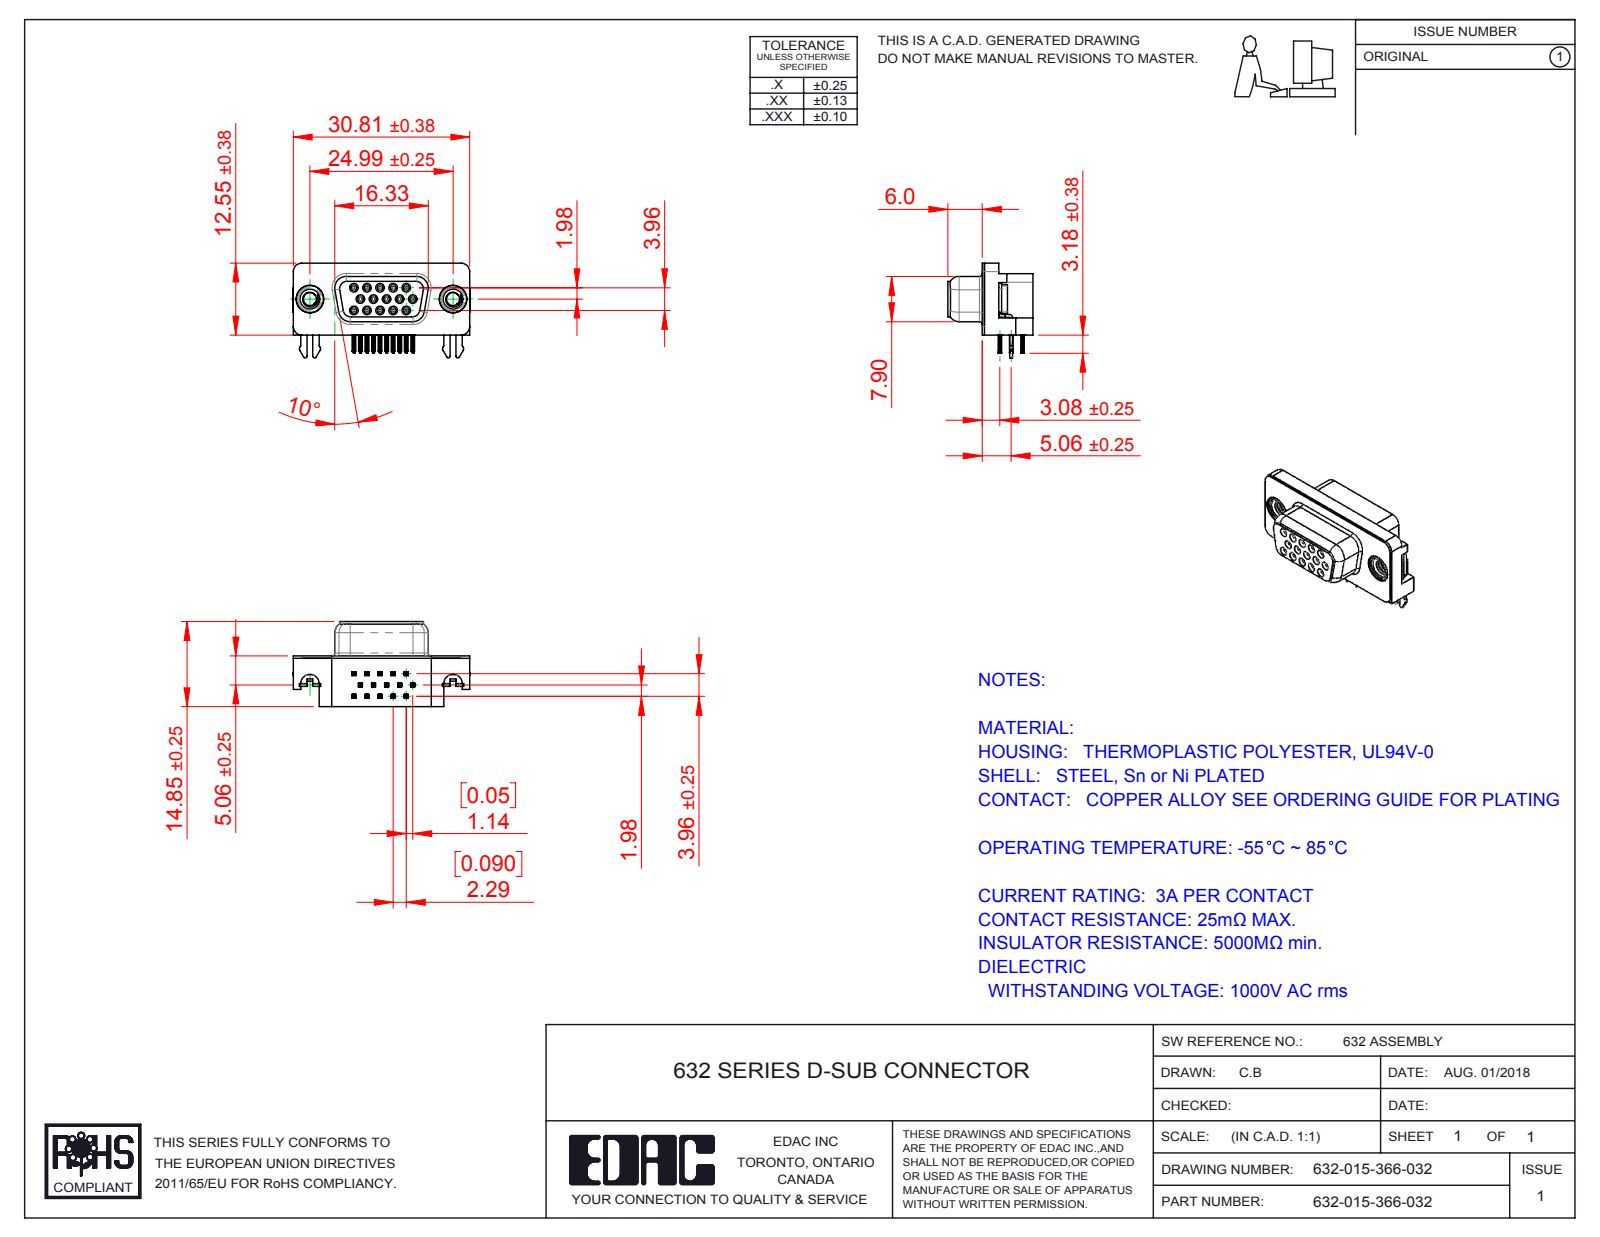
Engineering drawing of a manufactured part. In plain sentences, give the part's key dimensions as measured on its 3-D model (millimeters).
The part is named "632 Shell_9 Socket; 632 2 Prong Board Lock; 632 4-40 Threaded Rivet; 632 Contact Middle (+4 more)". Its 3-D file was written by "SolidWorks 2016 (CONFIG_CONTROL_DESIGN)". It is 21 solids with 2338 faces: 990 planar, 612 cylindrical and 736 other. Overall it measures 30.89 by 16.55 by 14.85 millimeters. Its volume is 2 921 cubic millimeters and its surface area 5 018 square millimeters. Round holes: 15 of diameter 0.8, 15 of diameter 0.9, 2 of diameter 2.26, 2 of diameter 4, 2 of diameter 4.8, 2 of diameter 5. Round bosses or shafts: 15 of diameter 1.2, 2 of diameter 4.9, 2 of diameter 4.75, 2 of diameter 3.9. Partial cylindrical surfaces (rounded edges, fillets, slot ends): 120 of radius 0.1, 60 of radius 0.15, 30 of radius 0.35, 15 of radius 0.34, 11 of radius 1, 10 of radius 0.28, 10 of radius 0.5, 8 of radius 0.25. The main face-to-face distances are 0.4, 1.98, 8.45, 8.85, 2.9, 2.5, 5.95, 6.4, 6.7, 7.05. The hole center spacings are 2.28, 2.29, 3.96, 4.57, 6.05, 3.97, 4.58, 6.86.
